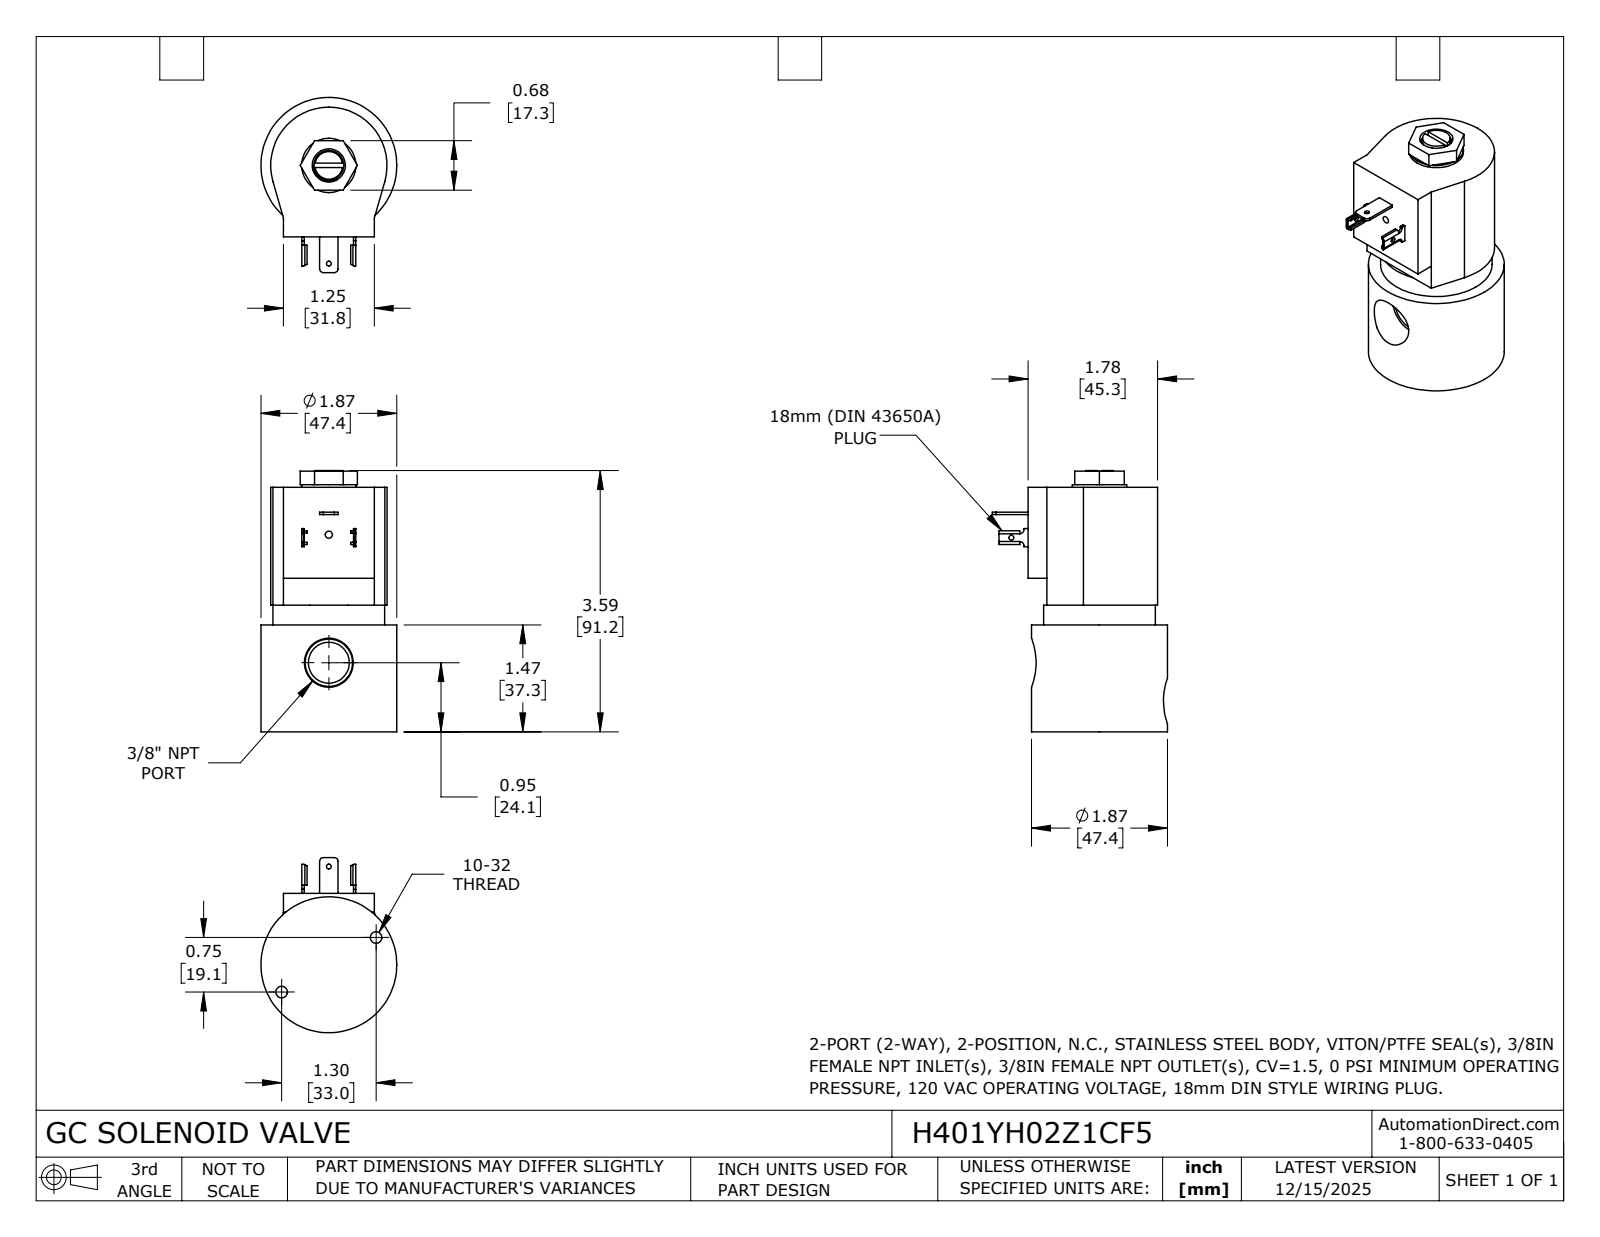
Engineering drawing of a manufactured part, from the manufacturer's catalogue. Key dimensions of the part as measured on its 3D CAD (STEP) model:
Part name (STEP PRODUCT): H401YH02Z1CF5
STEP written by: SolidWorks 2024 (CONFIG_CONTROL_DESIGN)
Units: inches
Bodies: 1 solid, 203 faces (80 planar, 98 cylindrical, 25 other)
Overall size (bounding box): 3.591 × 2.407 × 1.868
Volume: 7.989 in³ · Surface area: 30.19 in²
Round holes (diameter × count): ⌀0.159 ×2, ⌀0.562 ×2, ⌀0.066 ×1, ⌀0.067 ×1, ⌀0.1 ×1, ⌀0.456 ×1
Round bosses / shafts (diameter × count): ⌀1.868 ×1, ⌀1.535 ×1, ⌀0.746 ×1, ⌀0.38 ×1
Partial cylindrical surfaces — rounded edges, fillets, slot ends (radius × count): R0.006 ×4, R0.041 ×4, R0.05 ×2, R0.06 ×2, R0.8 ×1
Main face-to-face distances: 3.36, 1.47, 1.89, 0.26, 2.11, 0.64, 1.25, 1.25, 1.62, 3.583
Hole centre spacings: 0.75, 0.527, 1.171, 1.35, 1.5, 1.759, 1.843, 2.286
